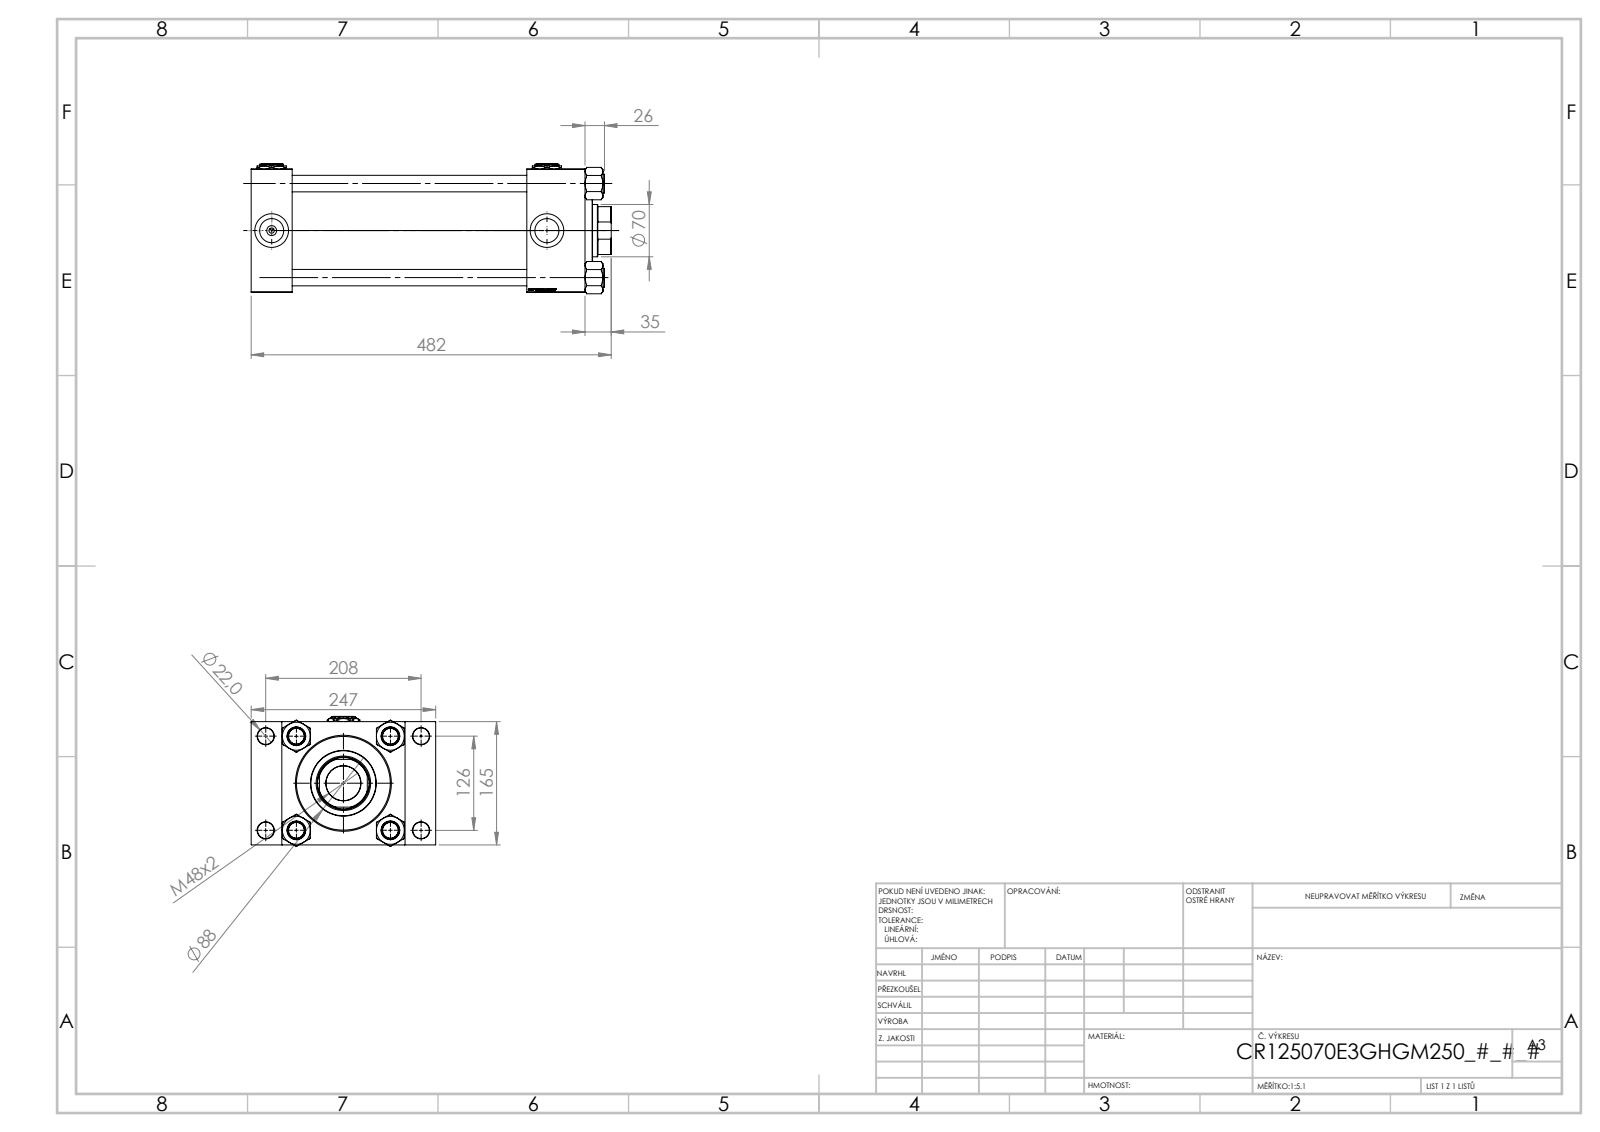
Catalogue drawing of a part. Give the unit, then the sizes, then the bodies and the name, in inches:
Units: inches
Overall size (bounding box): 18.976 × 9.724 × 6.853
Round holes (diameter × count): ⌀0.866 ×8, ⌀1.269 ×4, ⌀1.772 ×4, ⌀0.276 ×3, ⌀0.098 ×2, ⌀1.831 ×1, ⌀2.756 ×1, ⌀2.874 ×1, ⌀3.78 ×1, ⌀4.921 ×1, ⌀4.941 ×1
Round bosses / shafts (diameter × count): ⌀0.984 ×4, ⌀5.157 ×1, ⌀3.465 ×1
Partial cylindrical surfaces — rounded edges, fillets, slot ends (radius × count): R1.339 ×1
Main face-to-face distances: 2.165, 6.496, 17.598, 15.433, 1.614, 3.071, 14.528, 12.362, 8.11, 16.469
Hole centre spacings: 1.616, 2.48, 3.003, 3.505, 4.787, 4.957, 5.215, 5.473
Volume: 413.1 in³ · Surface area: 1 380 in²
Bodies: 13 solids, 1290 faces (595 planar, 101 cylindrical, 594 other)
Part name (STEP PRODUCT): V215CR_TYCINKA_E; V215_VC_A; V215CR_E_Body; V215CR_VCP_E (+2 more)
STEP written by: SolidWorks 2019 (CONFIG_CONTROL_DESIGN)
